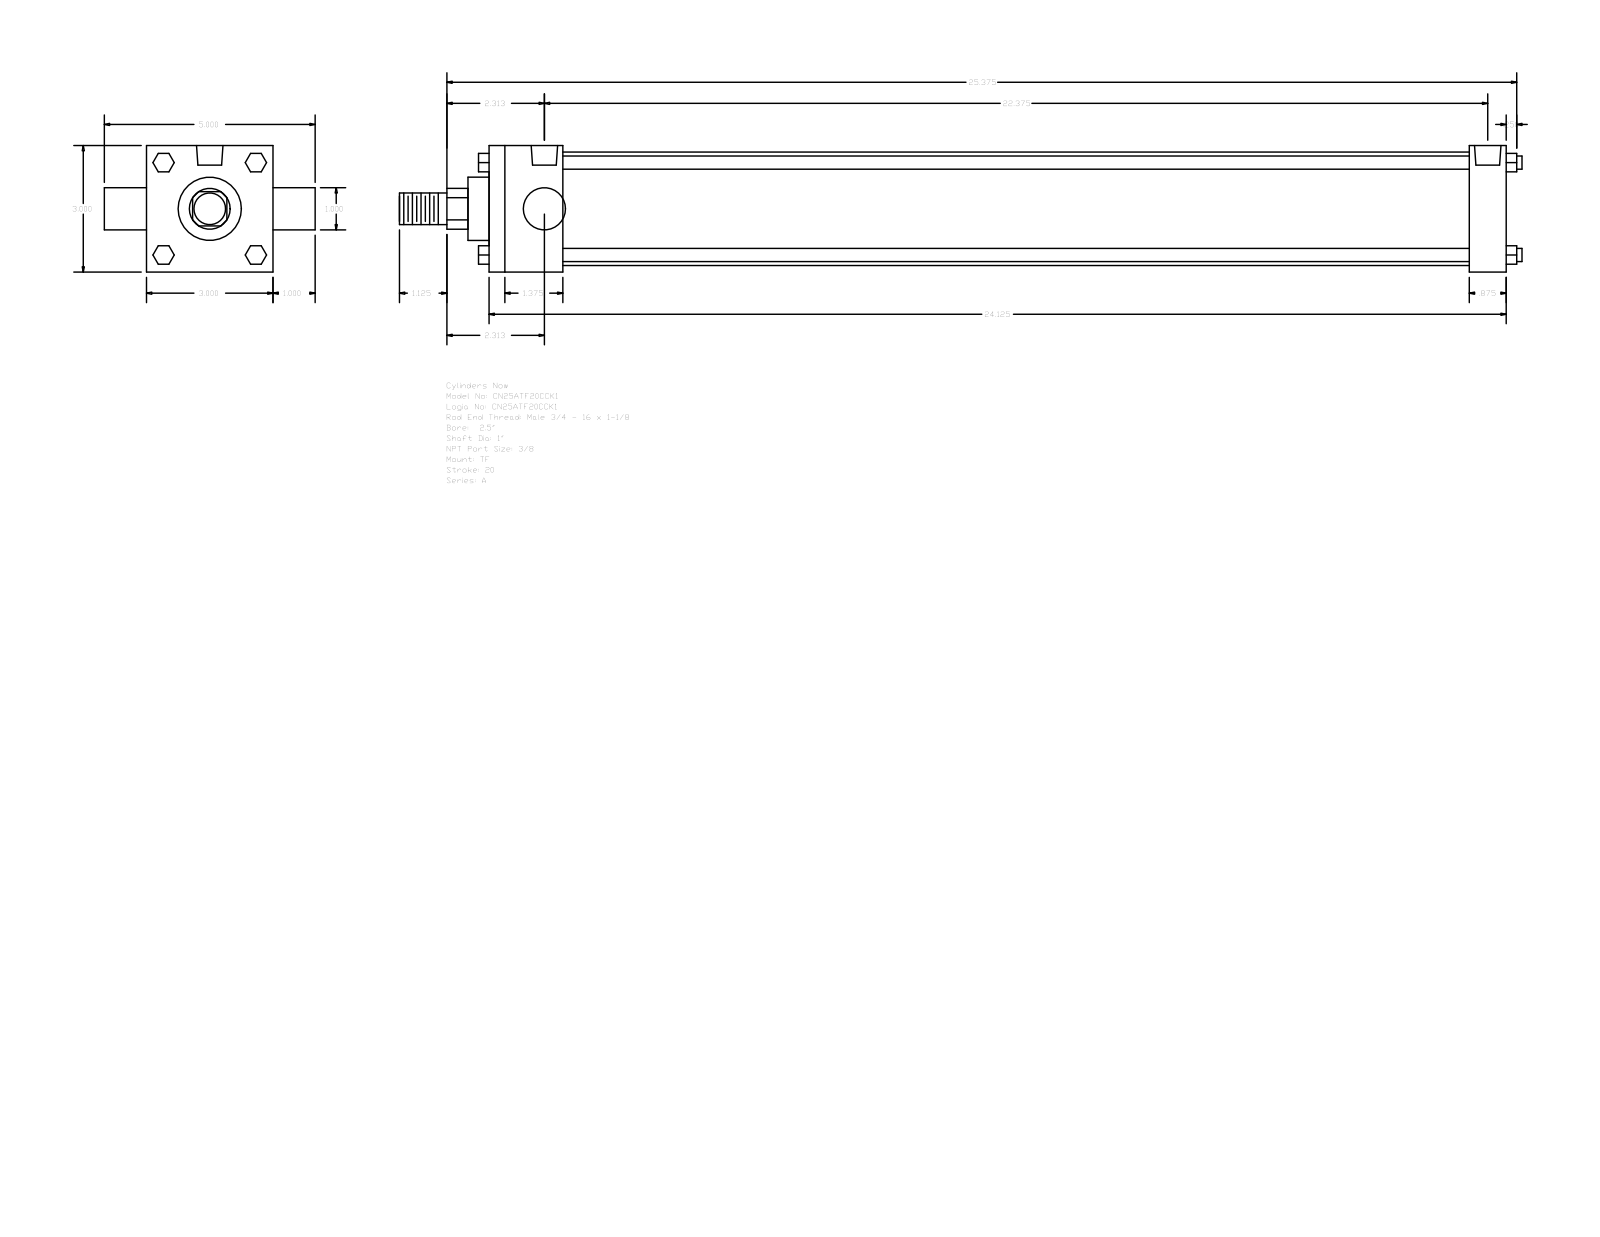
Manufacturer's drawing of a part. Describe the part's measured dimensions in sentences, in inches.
The part is named "A_TF__0250_1". Its 3-D file was written by "GSSL Pune (CONFIG_CONTROL_DESIGN)". It is 0 solids with 120 faces: 92 planar, 28 cylindrical and 0 other. Overall it measures 26.625 by 5 by 3 inches. Round holes: 3 of diameter 0.219, 2 of diameter 0.627. Round bosses or shafts: 4 of diameter 0.313, 2 of diameter 1, 1 of diameter 2.69, 1 of diameter 1.5, 1 of diameter 0.75. Partial cylindrical surfaces (rounded edges, fillets, slot ends): 1 of radius 0.484. The main face-to-face distances are 3, 24.125, 1.75, 23.25, 21.5, 22.375, 0.875, 1, 4, 24.625. The hole center spacings are 0.094, 22.469, 22.375, 22.562.
